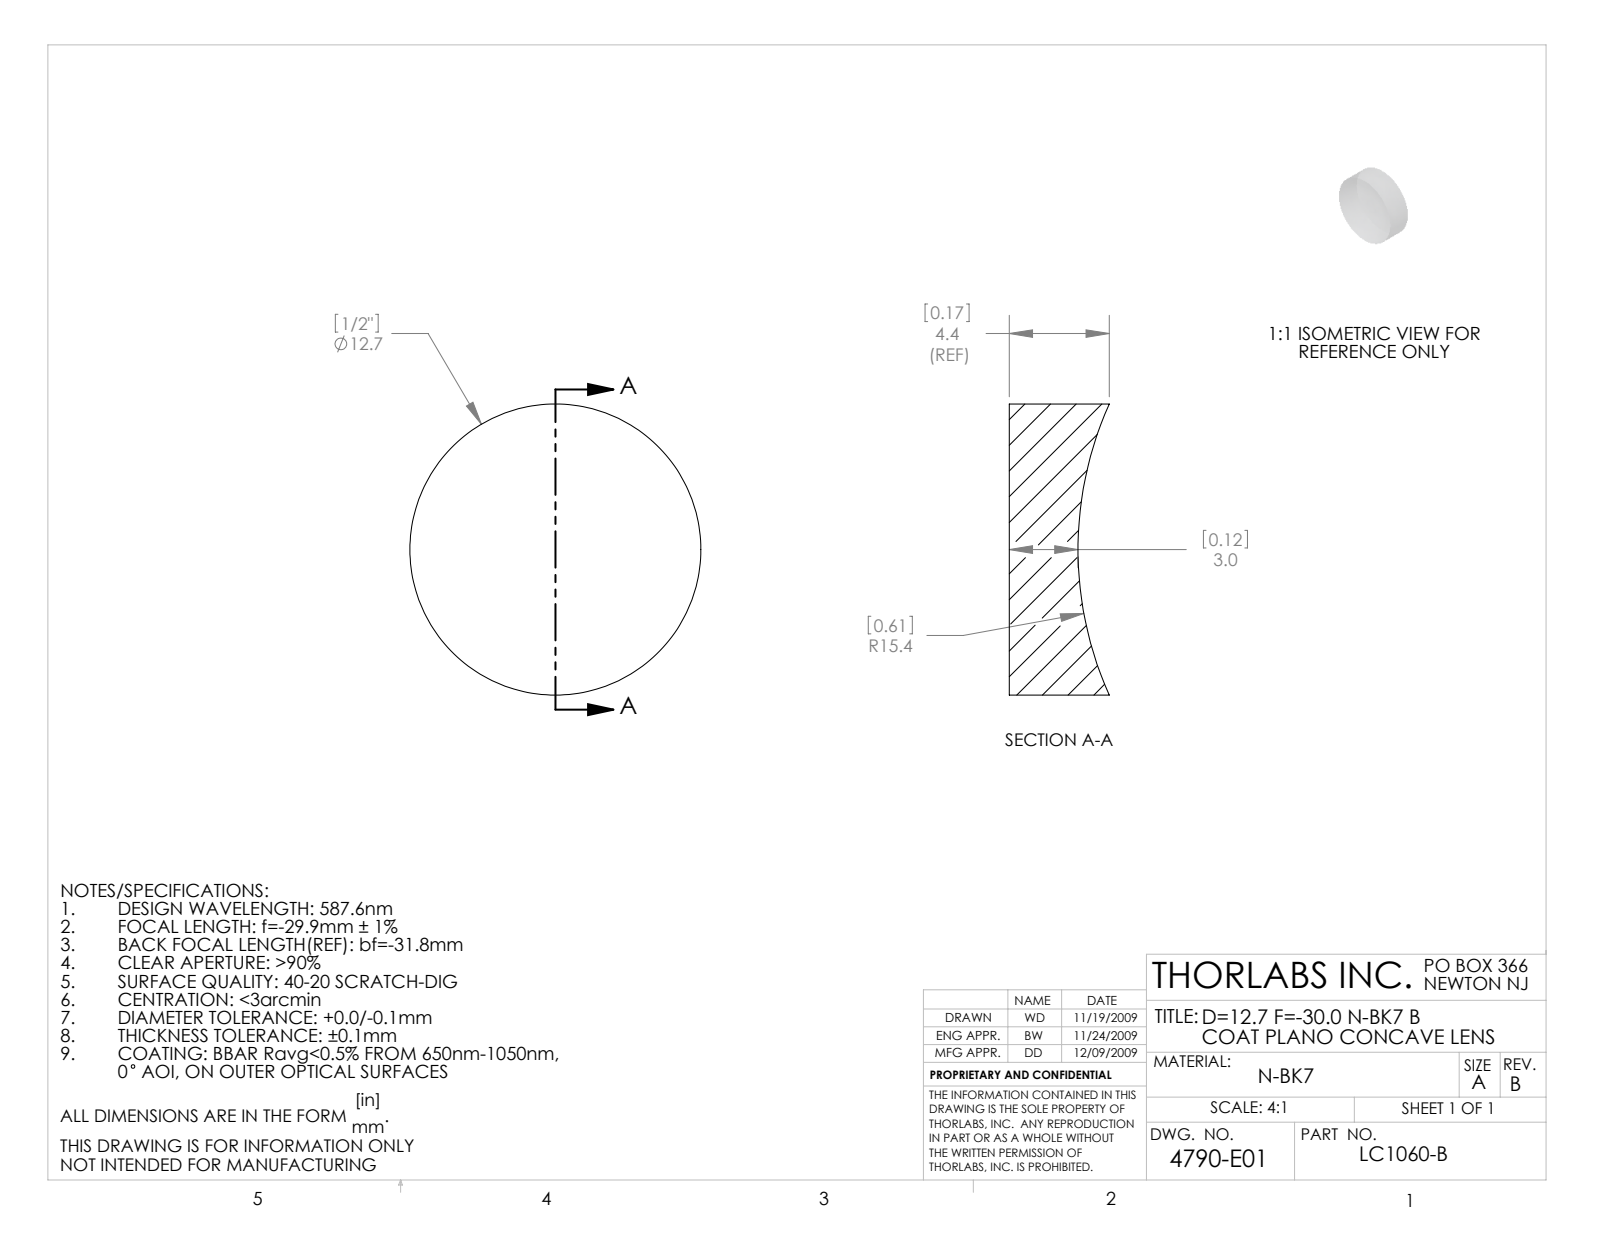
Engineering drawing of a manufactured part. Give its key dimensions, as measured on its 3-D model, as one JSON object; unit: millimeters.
{"part_name": "4790-E0W", "step_written_by": "SolidWorks 2009 (AUTOMOTIVE_DESIGN)", "units": "millimeters", "bodies": {"solids": 1, "faces": 5, "planar": 1, "cylindrical": 2, "other": 2}, "overall_size": [12.7, 12.7, 4.37], "volume_mm3": 465, "surface_area_mm2": 433, "round_bosses_or_shafts": [[12.7, 1]]}
